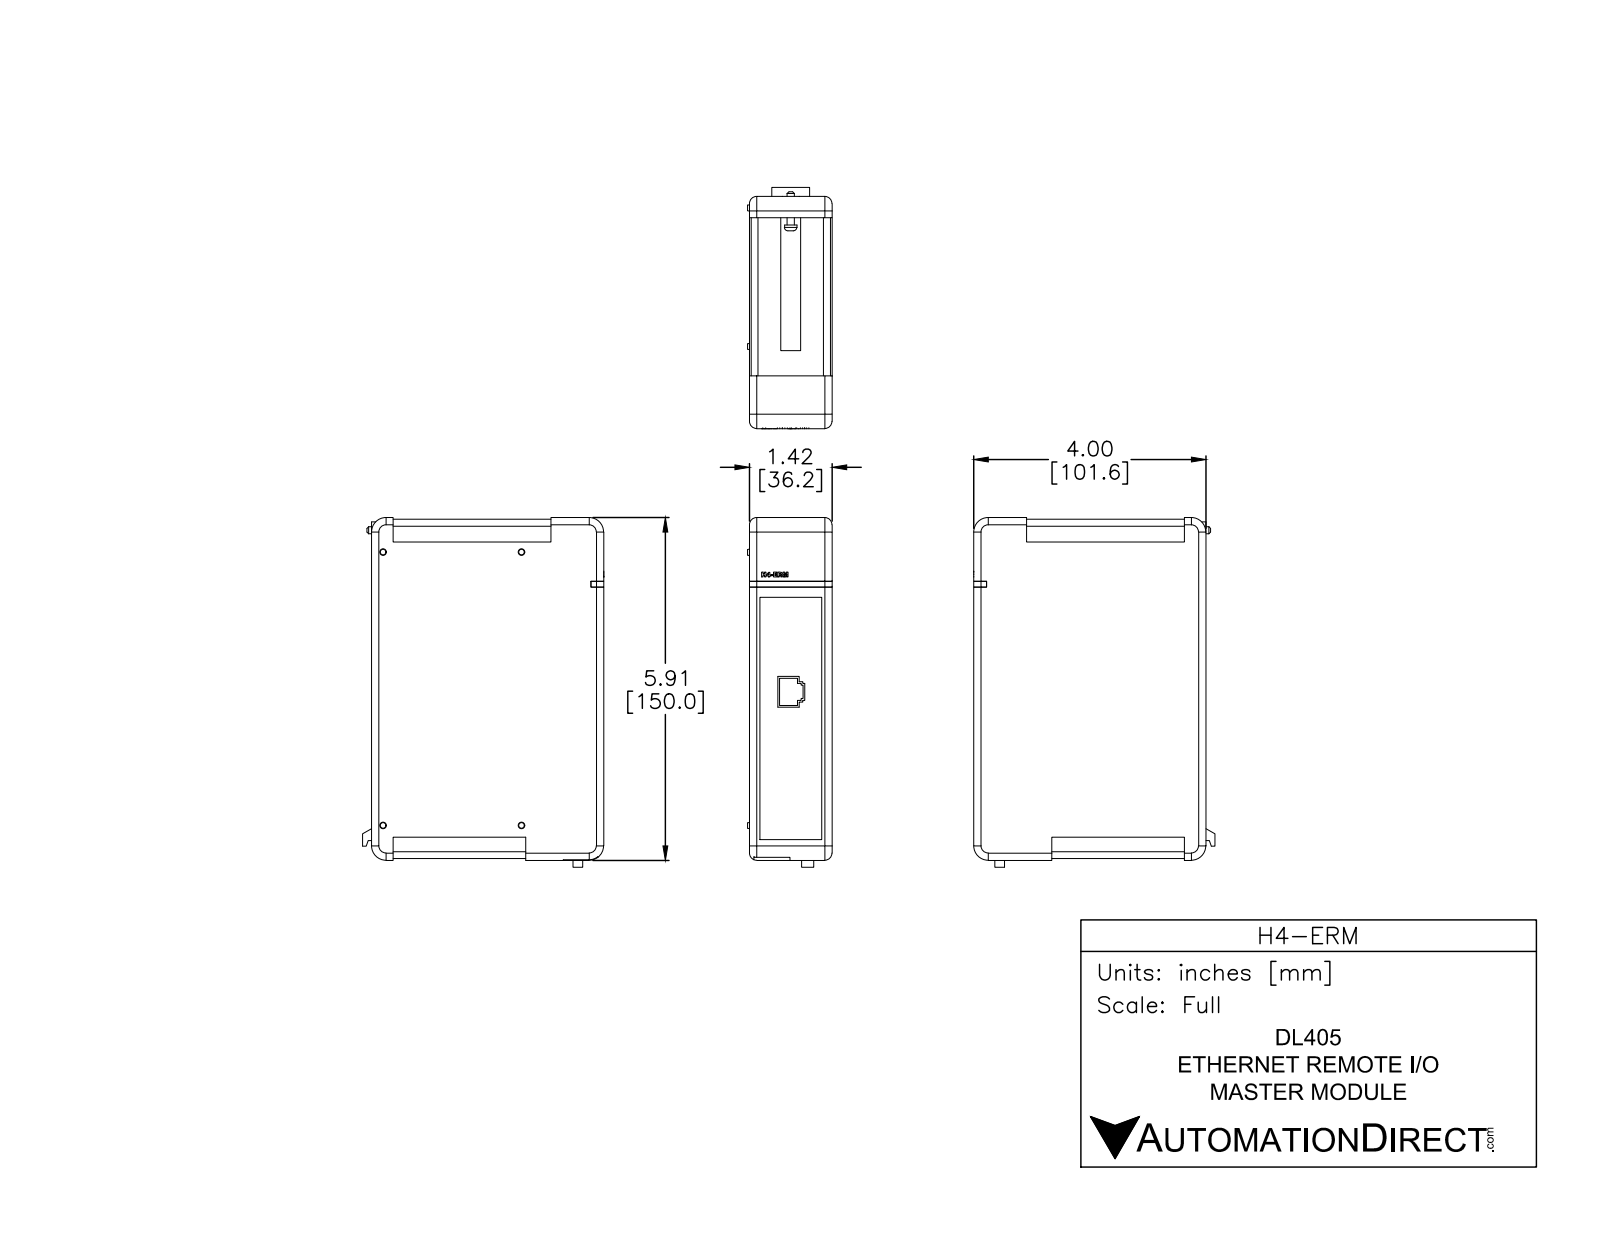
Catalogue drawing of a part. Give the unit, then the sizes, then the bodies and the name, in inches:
Units: inches
Overall size (bounding box): 6.025 × 4.156 × 1.455
Round bosses / shafts (diameter × count): ⌀0.212 ×1, ⌀0.123 ×1
Partial cylindrical surfaces — rounded edges, fillets, slot ends (radius × count): R0.125 ×8, R0.12 ×4, R0.25 ×4, R0.145 ×1, R0.171 ×1
Main face-to-face distances: 1.425, 0.03, 3.97, 1.395, 5.845, 5.875, 4, 0.2, 3.77, 3.8
Volume: 32.09 in³ · Surface area: 81.26 in²
Bodies: 2 solids, 263 faces (194 planar, 34 cylindrical, 35 other)
Part name (STEP PRODUCT): H4-ERM
STEP written by: SolidWorks 2014 (AUTOMOTIVE_DESIGN)
